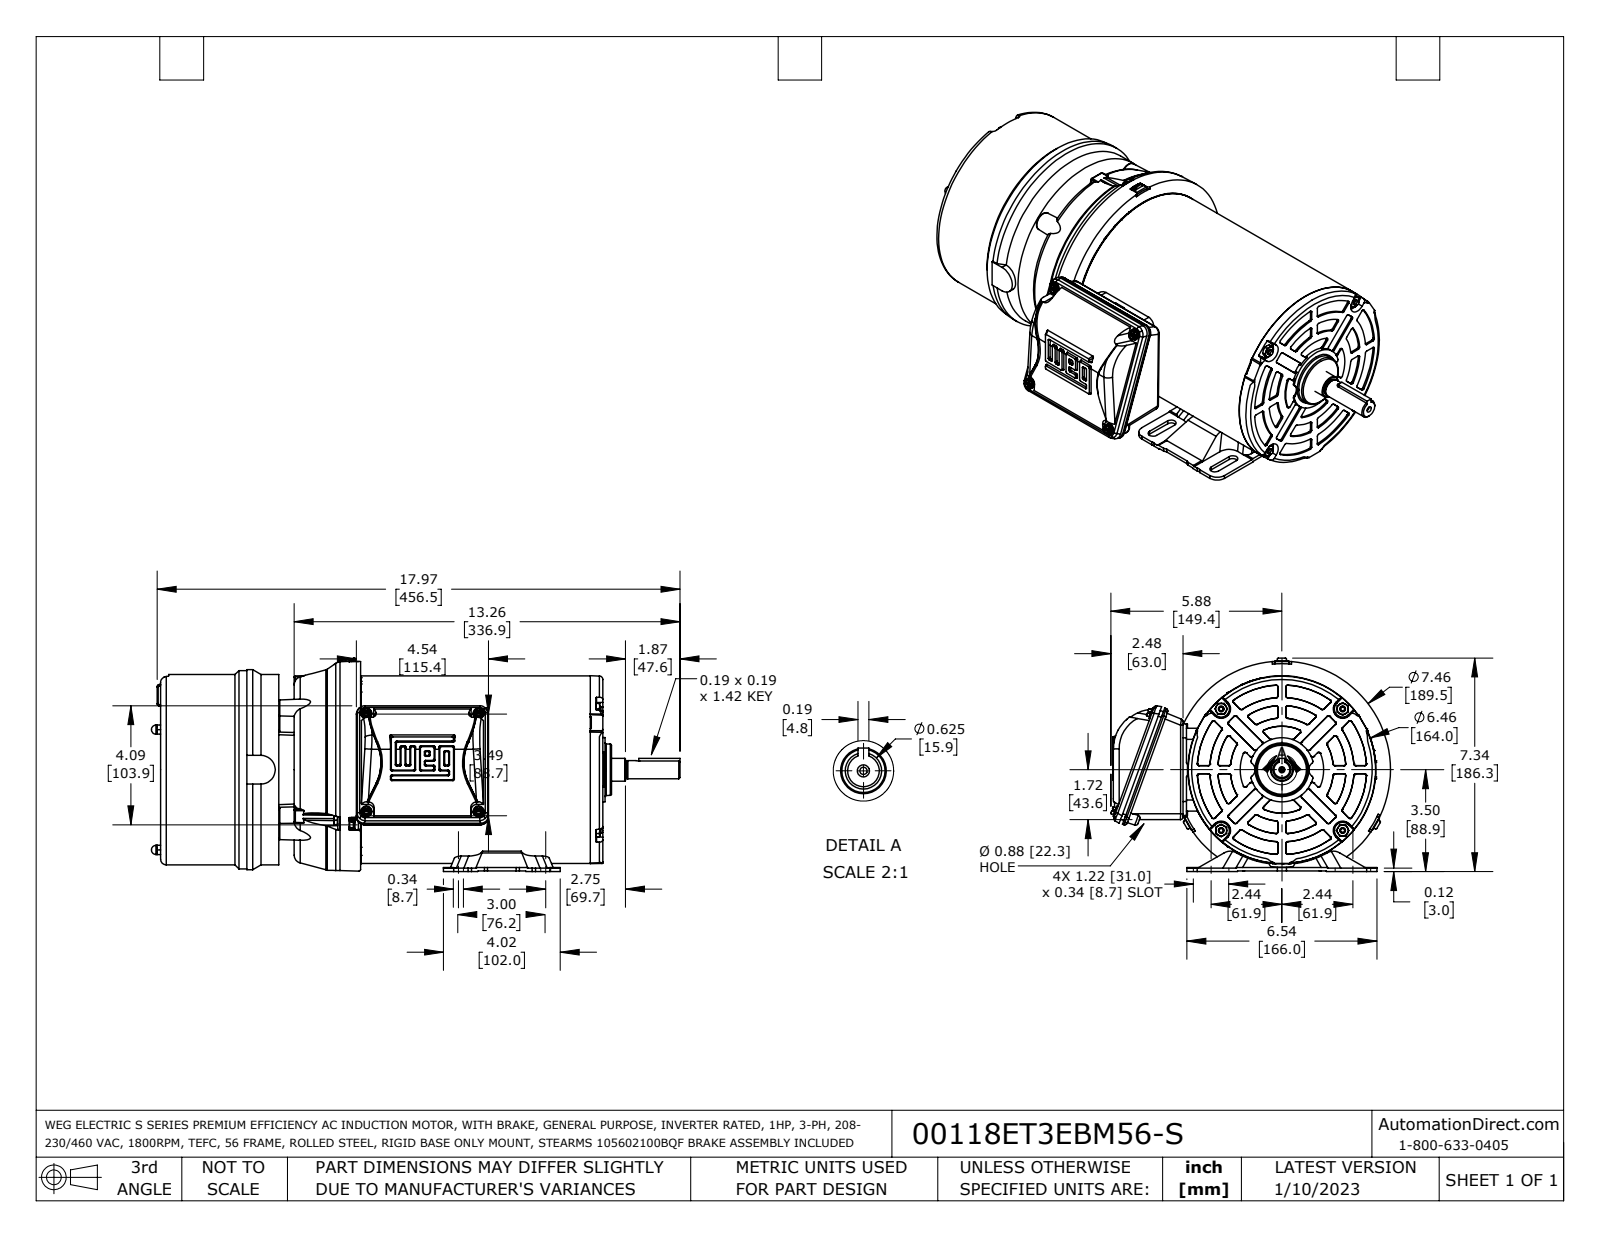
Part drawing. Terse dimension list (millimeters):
name: 56_3PH_TEFC_BM_18165 coord fxt
written by: SolidWorks 2021 (AUTOMOTIVE_DESIGN)
unit: mm
bodies: 22 solids, 1513 faces (568 planar, 404 cylindrical, 541 other)
size: 461.5 × 244.1 × 186.4
volume: 8 865 000 mm³; area: 518 600 mm²
holes: 4× ⌀4, 1× ⌀3.1
bosses: 4× ⌀9.5, 4× ⌀4.2, 3× ⌀8, 3× ⌀6.5, 1× ⌀174.5, 1× ⌀173, 1× ⌀166.1, 1× ⌀164
rounds: 47× R1, 40× R1.2, 22× R0.5, 16× R1.5, 16× R2, 12× R2.2, 10× R7, 8× R0.6
face distances: 200, 272, 72, 13.5, 103.1, 175.1, 375.1, 116.6, 58.5, 258.5
hole spacings: 75, 106.1, 150
